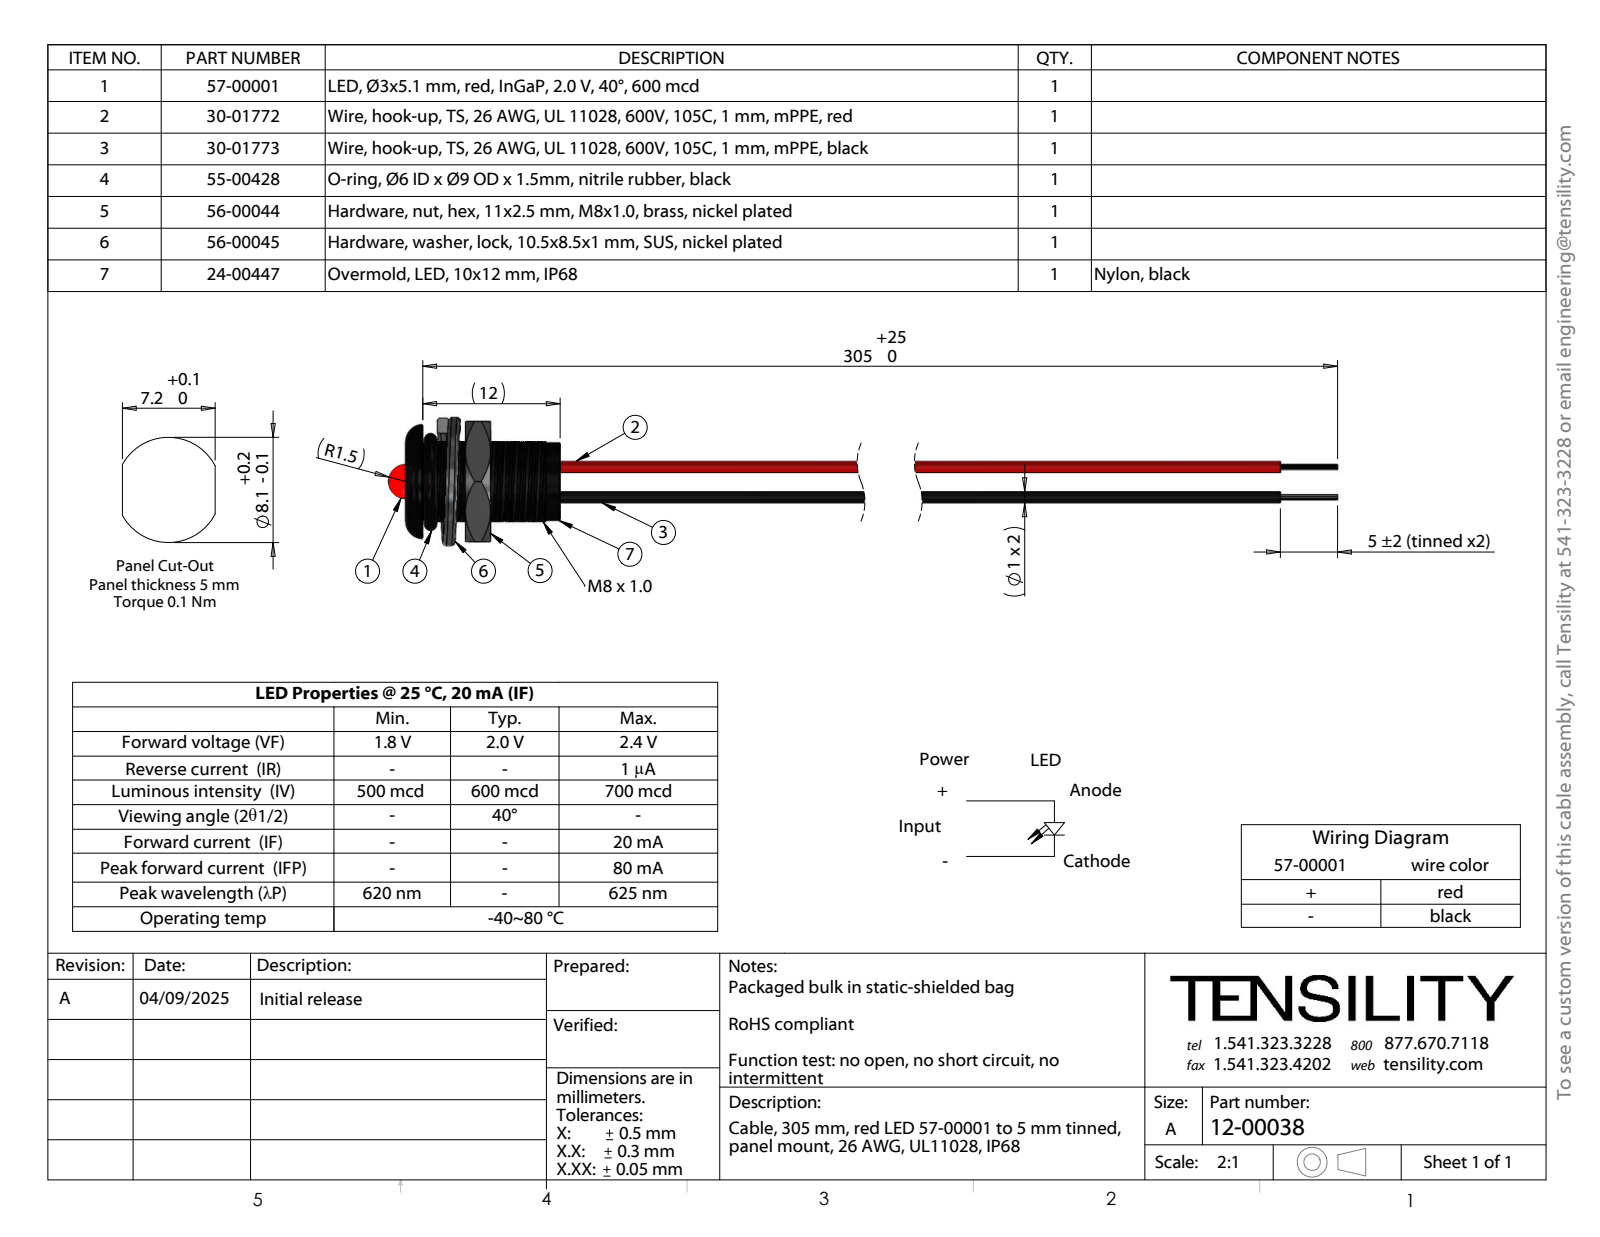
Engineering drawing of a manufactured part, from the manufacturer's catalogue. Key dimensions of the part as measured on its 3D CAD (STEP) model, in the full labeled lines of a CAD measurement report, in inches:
Part name (STEP PRODUCT): 56-00045_Split washer; 30-01772_stripped and tinned; 24-00447; 12-00038 (+4 more)
STEP written by: SolidWorks 2021 (CONFIG_CONTROL_DESIGN)
Units: inches
Bodies: 57 solids, 555 faces (186 planar, 246 cylindrical, 123 other)
Overall size (bounding box): 6.693 × 0.477 × 0.441
Volume: 0.061 in³ · Surface area: 9.157 in²
Round holes (diameter × count): ⌀0.039 ×2
Round bosses / shafts (diameter × count): ⌀0.039 ×2, ⌀0.02 ×2, ⌀0.268 ×1, ⌀0.118 ×1
Partial cylindrical surfaces — rounded edges, fillets, slot ends (radius × count): R0.137 ×1, R0.157 ×1
Main face-to-face distances: 0.059, 0.531, 0.472, 0.413, 0.205, 0.146, 0.326, 0.292, 0.233, 0.087
Hole centre spacings: 0.014, 0.015, 0.013, 0.098, 0.099, 0.096, 0.096, 0.101
